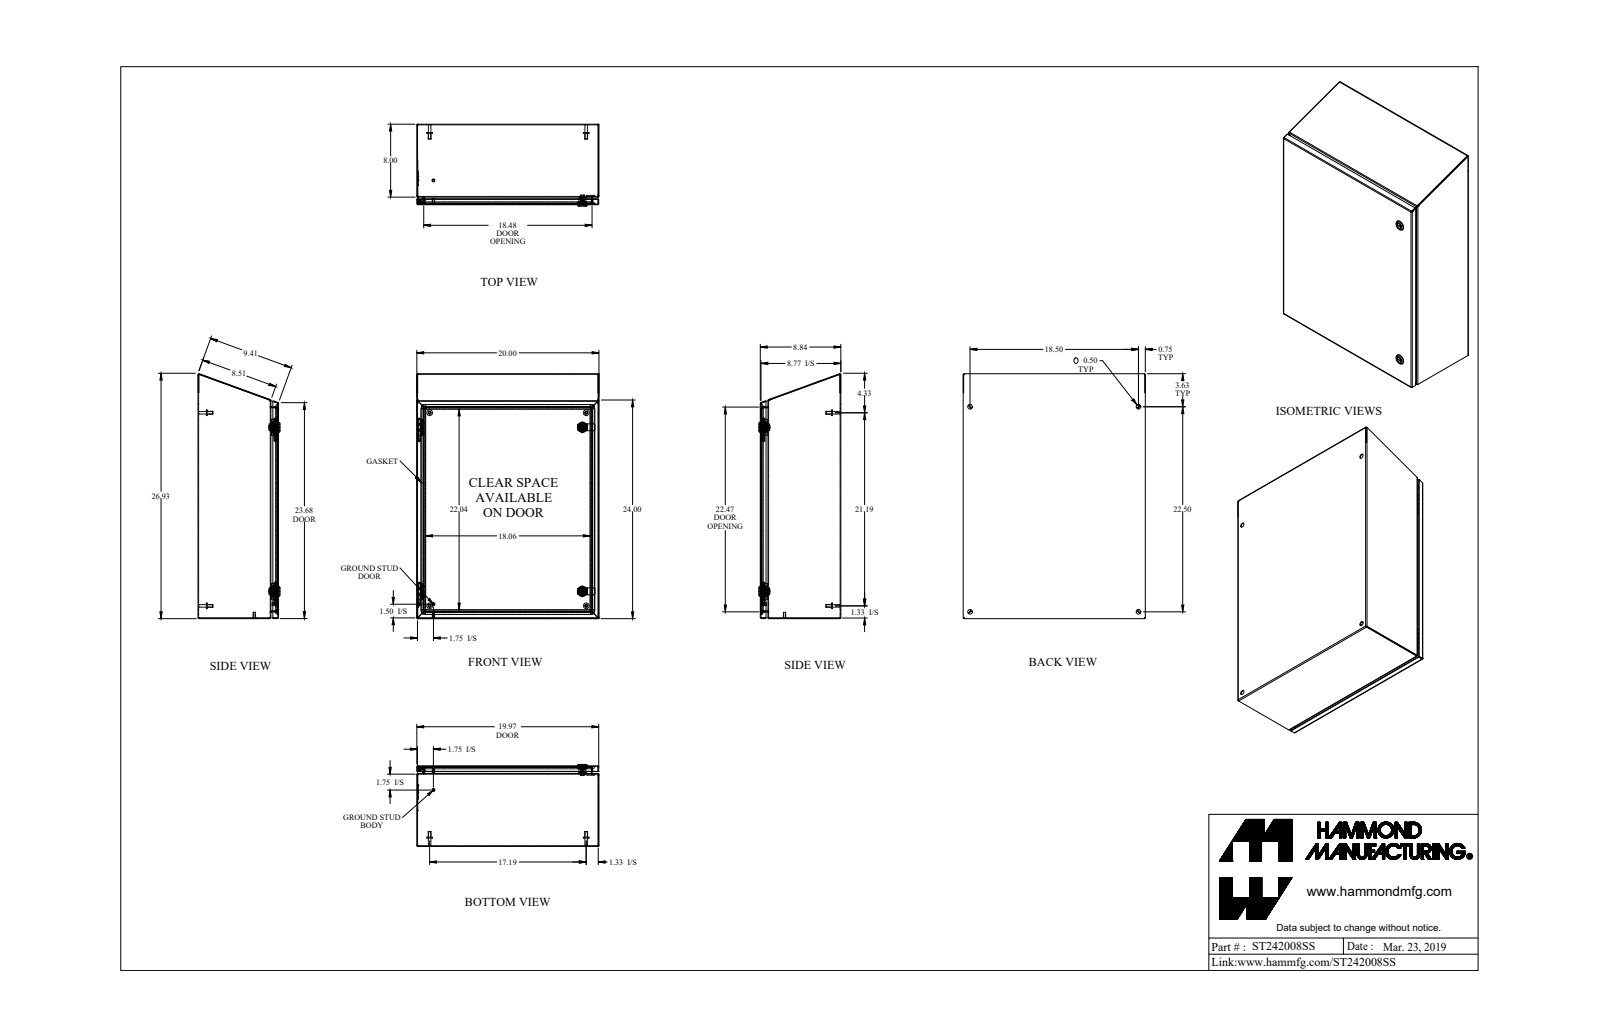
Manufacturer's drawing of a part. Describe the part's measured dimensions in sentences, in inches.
The part is named "ST242008SS". Its 3-D file was written by "SolidWorks 2018 (AUTOMOTIVE_DESIGN)". It is 27 solids with 776 faces: 410 planar, 230 cylindrical and 136 other. Overall it measures 26.883 by 20 by 8.997 inches. Its volume is 147 cubic inches and its surface area 4 048 square inches. Round holes: 6 of diameter 0.5, 2 of diameter 0.197, 2 of diameter 0.387, 2 of diameter 0.63, 2 of diameter 0.768, 1 of diameter 0.172, 1 of diameter 0.24, 1 of diameter 0.242. Round bosses or shafts: 6 of diameter 0.625, 6 of diameter 0.313, 4 of diameter 0.275, 2 of diameter 1.1, 2 of diameter 0.785, 2 of diameter 0.525, 2 of diameter 0.25, 2 of diameter 0.236. Partial cylindrical surfaces (rounded edges, fillets, slot ends): 20 of radius 0.036, 20 of radius 0.108, 11 of radius 0.25, 4 of radius 0.006, 4 of radius 0.062, 4 of radius 0.125, 4 of radius 0.499, 2 of radius 0.307. The main face-to-face distances are 0.072, 8.765, 8.693, 8.837, 19.928, 19.856, 20, 7.928, 0.837, 0.909. The hole center spacings are 2.493, 17.57, 18.5, 20.278, 22.5, 26.716, 29.129, 18.
